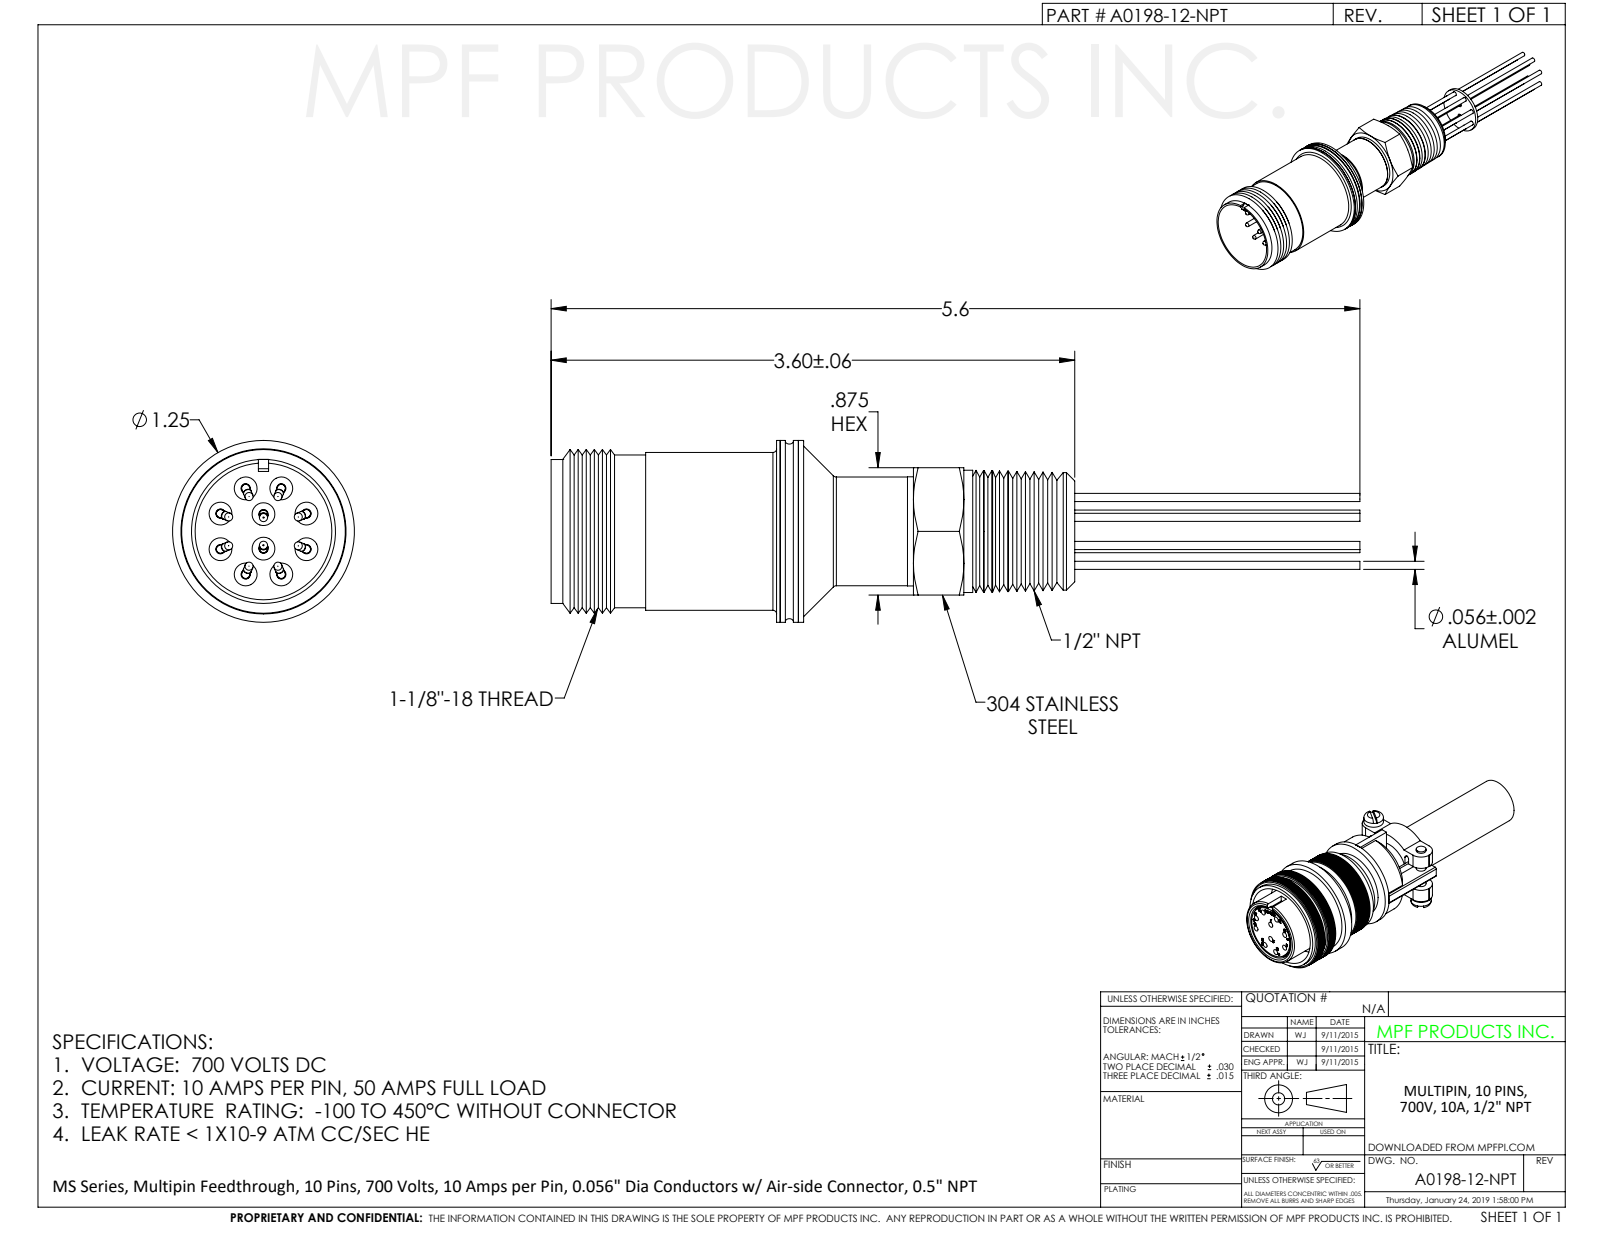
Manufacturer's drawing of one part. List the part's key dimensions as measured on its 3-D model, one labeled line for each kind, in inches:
Part name (STEP PRODUCT): A0198-12-NPT
STEP written by: SolidWorks 2011 (CONFIG_CONTROL_DESIGN)
Units: inches
Bodies: 0 solids, 269 faces (35 planar, 100 cylindrical, 134 other)
Overall size (bounding box): 5.56 × 1.25 × 1.25
Round holes (diameter × count): ⌀0.06 ×16, ⌀0.75 ×1, ⌀0.84 ×1, ⌀1 ×1, ⌀1.05 ×1, ⌀1.085 ×1
Round bosses / shafts (diameter × count): ⌀0.056 ×20, ⌀1.25 ×1, ⌀0.94 ×1, ⌀0.747 ×1, ⌀0.625 ×1, ⌀0.62 ×1
Main face-to-face distances: 0.125, 0.875, 2.559, 2.683, 0.04, 2.519, 2.643, 0.04, 0.535, 0.575
Hole centre spacings: 0.193, 0.252, 0.357, 0.467, 0.169, 0.233, 0.302, 0.342
